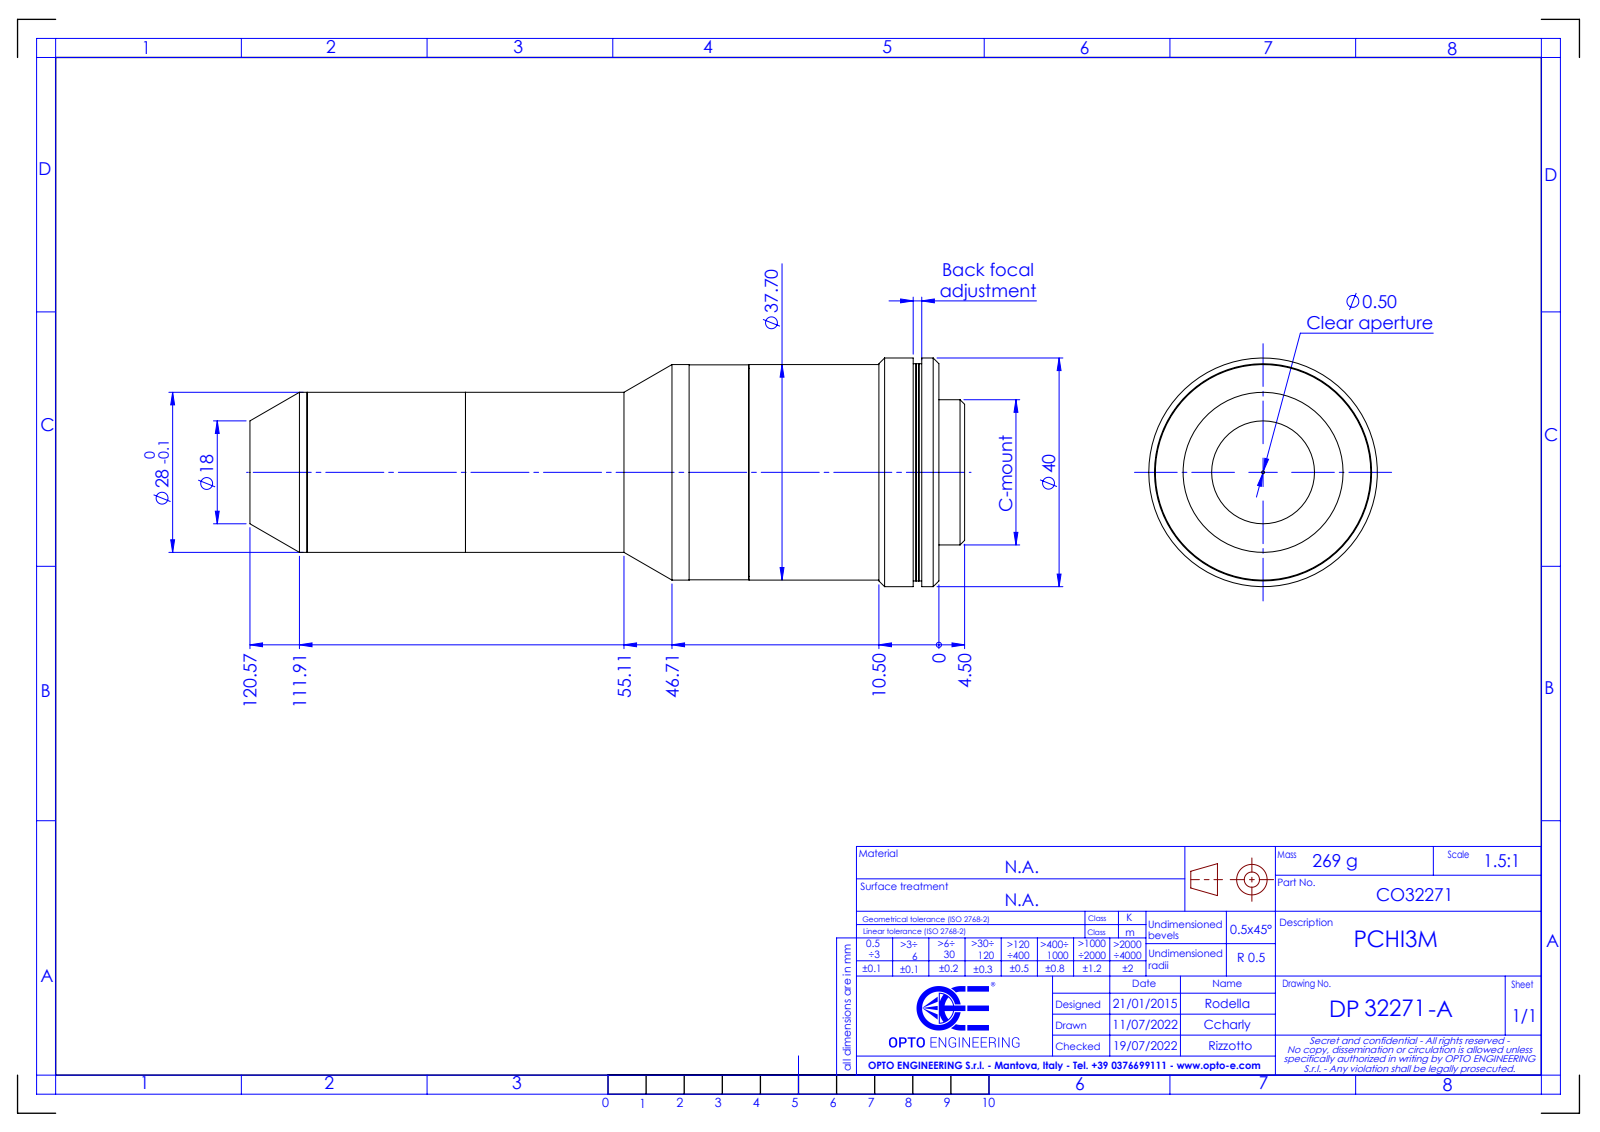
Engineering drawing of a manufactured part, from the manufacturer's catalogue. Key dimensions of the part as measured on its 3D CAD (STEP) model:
Part name (STEP PRODUCT): DP32271-A_PCHI3M
STEP written by: SolidWorks 2021 (CONFIG_CONTROL_DESIGN)
Units: millimetres
Bodies: 0 solids, 56 faces (14 planar, 30 cylindrical, 12 other)
Overall size (bounding box): 125.07 × 40 × 40
Round holes (diameter × count): ⌀0.5 ×1, ⌀13 ×1, ⌀22.5 ×1
Round bosses / shafts (diameter × count): ⌀40 ×1, ⌀38 ×1, ⌀37.7 ×1, ⌀37.6 ×1, ⌀28 ×1, ⌀25.4 ×1
Main face-to-face distances: 4.5, 3, 7.5, 1.5, 33.22, 25.72, 28.72, 30.22, 77.35, 103.07
